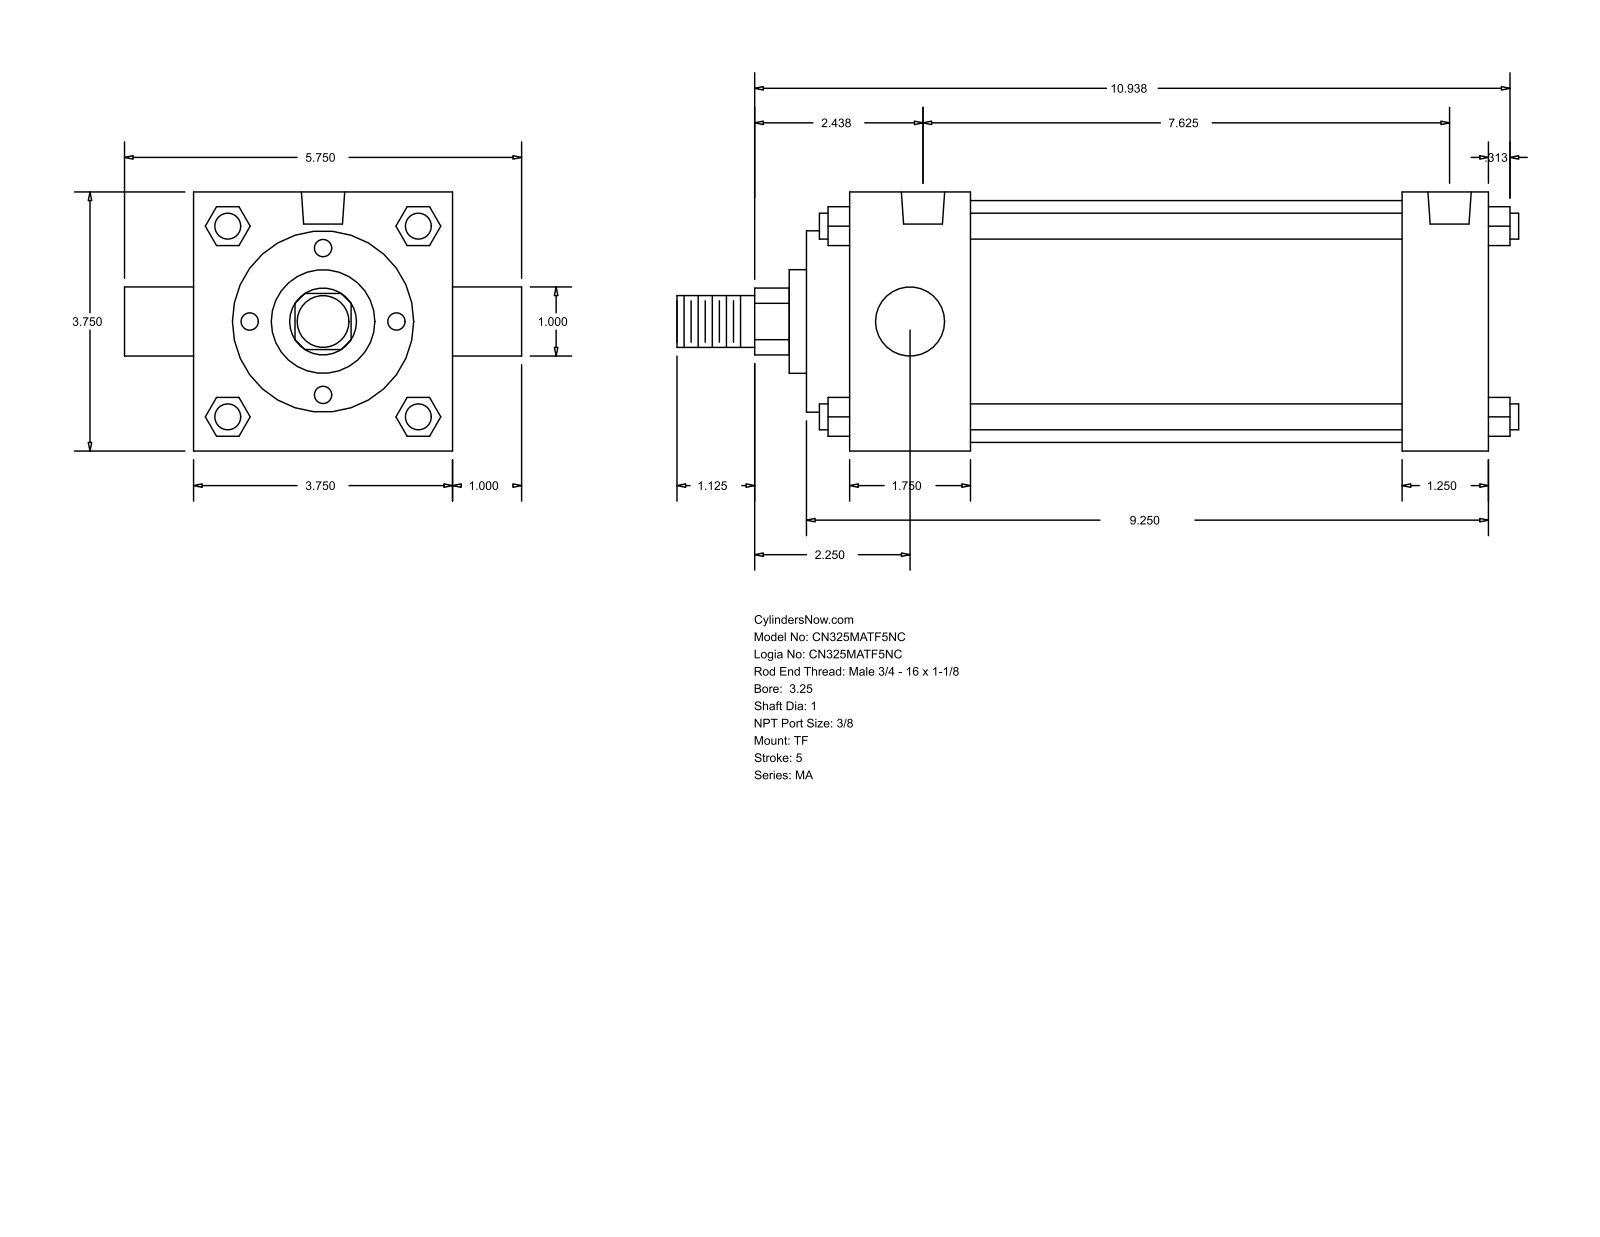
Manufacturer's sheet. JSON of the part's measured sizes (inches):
{"part_name": "MA_TF__0325_1", "step_written_by": "GSSL Pune (CONFIG_CONTROL_DESIGN)", "units": "inches", "bodies": {"solids": 0, "faces": 122, "planar": 93, "cylindrical": 29, "other": 0}, "overall_size": [12.187, 5.75, 3.75], "round_holes": [[0.437, 3], [0.627, 2]], "round_bosses_or_shafts": [[0.375, 4], [1, 2], [3.5, 1], [2.625, 1], [1.5, 1], [0.75, 1]], "partial_cylinders_radius": [[0.484, 1]], "face_to_face_distances": [3.75, 9.25, 1.75, 8, 6.25, 7.5, 1.25, 0.625, 2.375, 8.625], "hole_center_spacings": [0.187, 0.188, 7.25, 7.437, 7.438, 7.625]}
